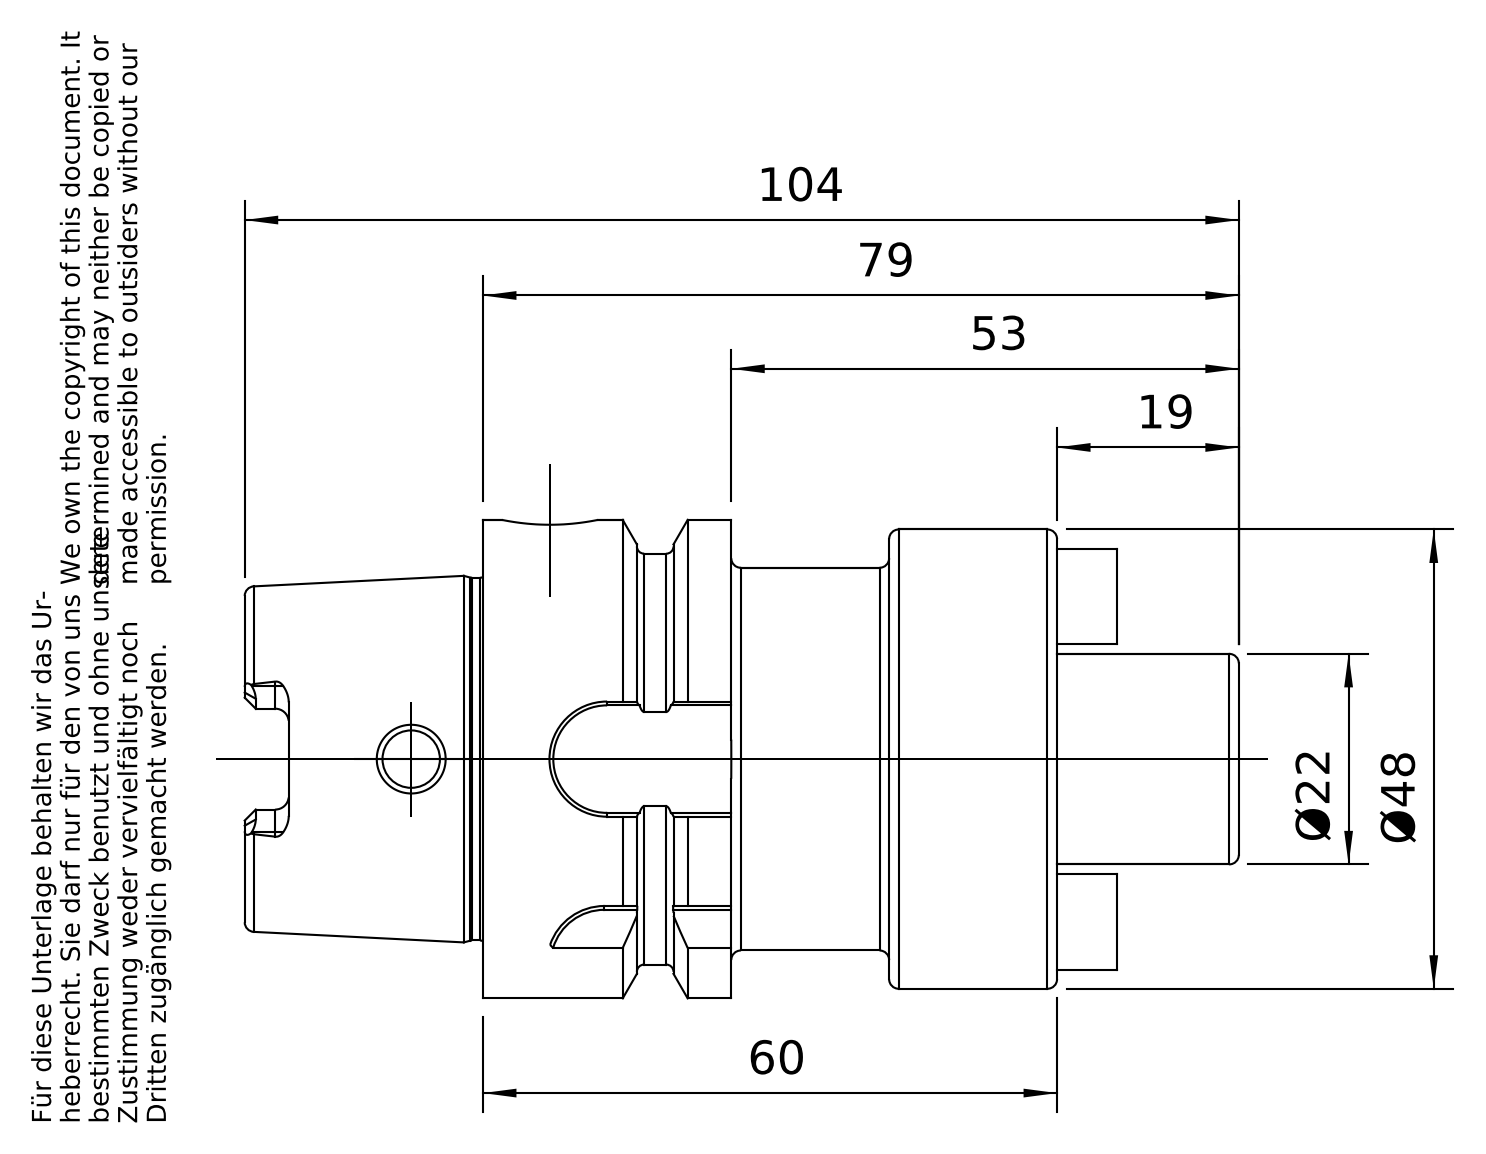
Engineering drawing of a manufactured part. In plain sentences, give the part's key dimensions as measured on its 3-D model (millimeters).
The part is named "A50-050-22". Its 3-D file was written by "PRO/ENGINEER BY PARAMETRIC TECHNOLOGY CORPORATION, 2010430 (CONFIG_CONTROL_DESIGN)". It is 1 solid with 209 faces: 76 planar, 55 cylindrical and 78 other. Overall it measures 103.9 by 50 by 50 millimeters. Its volume is 108 067 cubic millimeters and its surface area 24 210 square millimeters. Round holes: 2 of diameter 10, 1 of diameter 6, 1 of diameter 8.5, 1 of diameter 14, 1 of diameter 16, 1 of diameter 16.32, 1 of diameter 16.5, 1 of diameter 26.04, 1 of diameter 32.08. Round bosses or shafts: 1 of diameter 50, 1 of diameter 48, 1 of diameter 42.95, 1 of diameter 40, 1 of diameter 37.91, 1 of diameter 22. Partial cylindrical surfaces (rounded edges, fillets, slot ends): 6 of radius 1.4, 4 of radius 2.38, 3 of radius 6, 1 of radius 6.02. The main face-to-face distances are 60, 25.95, 34.05, 10, 42.45, 16.5, 17.55, 19, 53.05, 79.
